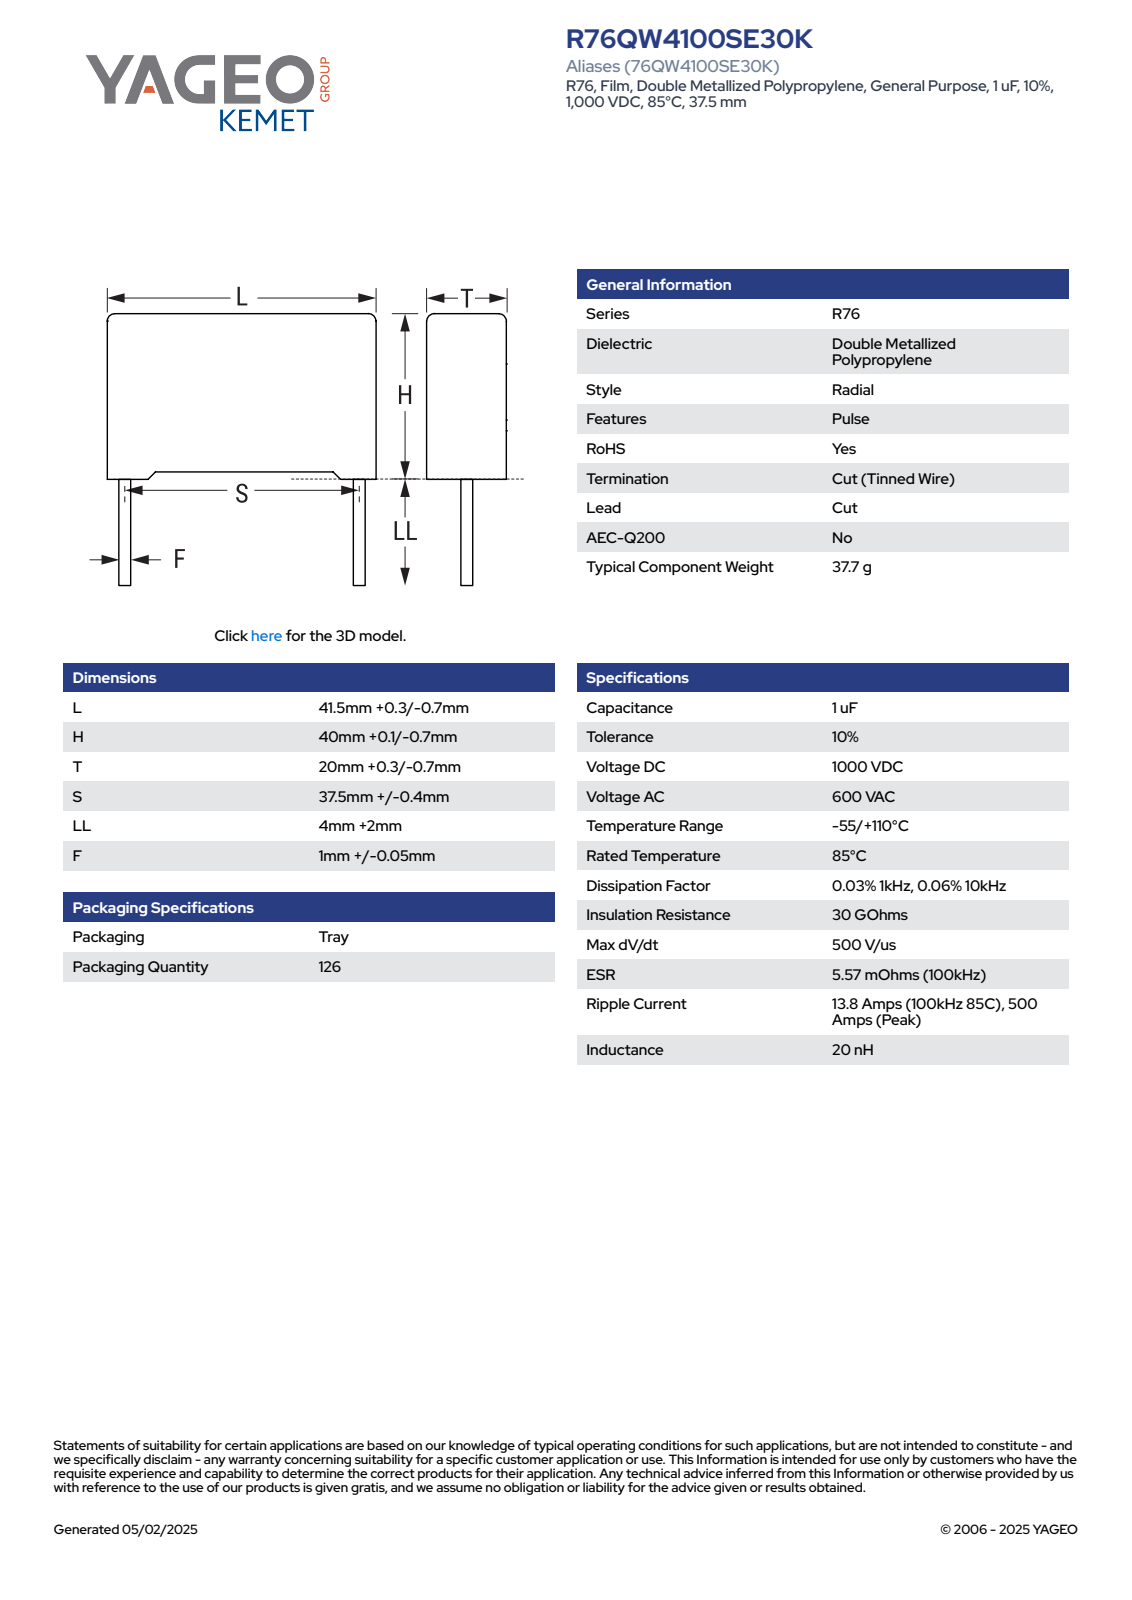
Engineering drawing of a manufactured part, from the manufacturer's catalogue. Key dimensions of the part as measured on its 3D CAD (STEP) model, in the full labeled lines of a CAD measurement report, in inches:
Part name (STEP PRODUCT): CFR_RB2_41.5X40X20_L41.8H40.1T20.3S37.5LL6F1.05
STEP written by: SolidWorks 2021 (AUTOMOTIVE_DESIGN)
Units: inches
Bodies: 4 solids, 85 faces (77 planar, 8 cylindrical, 0 other)
Overall size (bounding box): 1.815 × 1.646 × 0.799
Volume: 2.016 in³ · Surface area: 10.51 in²
Round bosses / shafts (diameter × count): ⌀0.041 ×2
Partial cylindrical surfaces — rounded edges, fillets, slot ends (radius × count): R0.02 ×4
Main face-to-face distances: 0.799, 1.646, 1.524, 0.025, 1.549, 0.03, 0.054, 1.579, 0.055, 0.8
